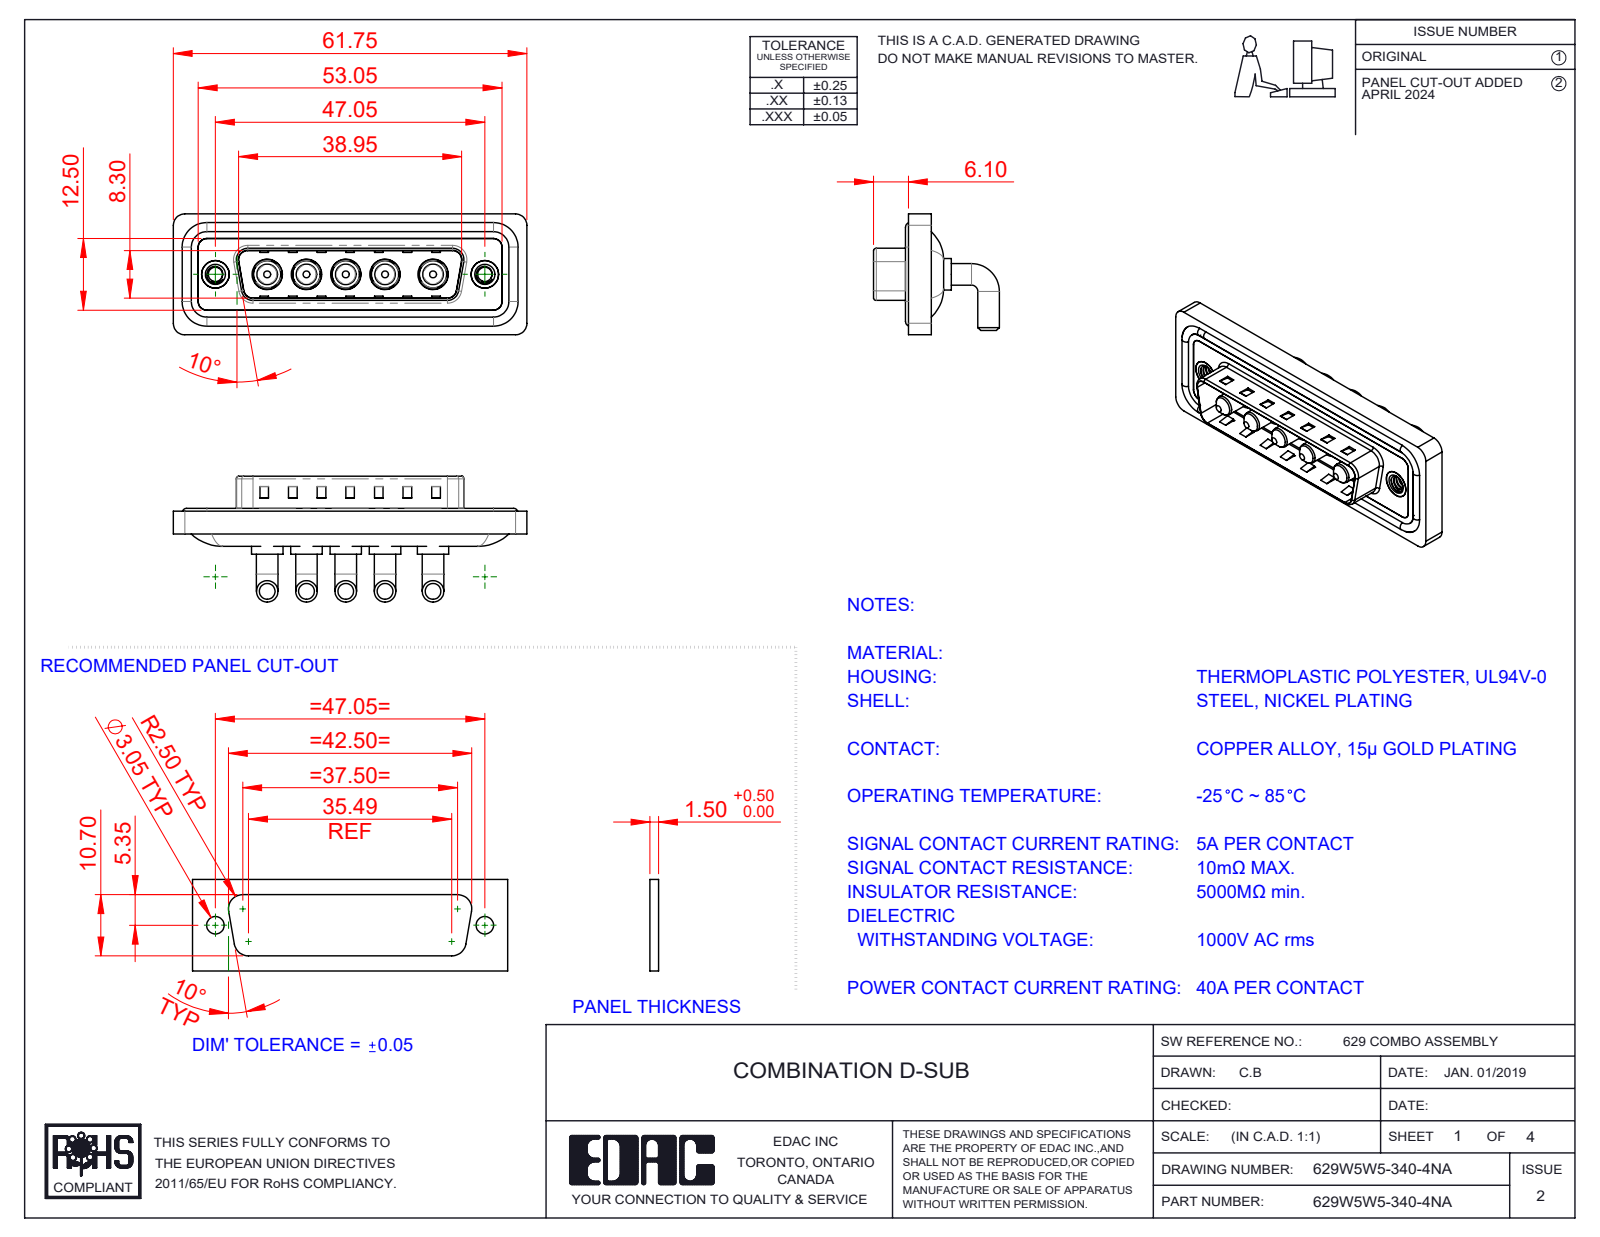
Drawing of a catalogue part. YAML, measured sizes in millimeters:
part_name: "629W5W5-340-4NA; 629Combo Waterproof Housing_25 Contacts; 629Combo Shell Rear_25 Contacts; 629Combo Threaded Rivet_A (+3 more)"
step_written_by: "SolidWorks 2023 (CONFIG_CONTROL_DESIGN)"
units: millimeters
bodies: {solids: 17, faces: 692, planar: 259, cylindrical: 291, other: 142}
overall_size: [61.75, 21.98, 21.1]
volume: 8170
surface_area: 12495
round_holes:
  - {diameter: 4.85, count: 5}
  - {diameter: 5.3, count: 5}
  - {diameter: 2.5, count: 2}
  - {diameter: 4, count: 2}
  - {diameter: 4.8, count: 2}
  - {diameter: 5, count: 2}
round_bosses_or_shafts:
  - {diameter: 3.75, count: 10}
  - {diameter: 5.5, count: 5}
  - {diameter: 5.2, count: 5}
  - {diameter: 4.75, count: 5}
  - {diameter: 3.6, count: 5}
  - {diameter: 1.6, count: 4}
  - {diameter: 4.9, count: 2}
partial_cylinders:
  - {radius: 1.5, count: 18}
  - {radius: 2, count: 18}
  - {radius: 0.5, count: 8}
  - {radius: 1.6, count: 8}
  - {radius: 2.1, count: 5}
  - {radius: 0.25, count: 4}
  - {radius: 0.6, count: 4}
  - {radius: 0.65, count: 4}
face_to_face_distances: [0.4, 2.9, 0.8, 4.5, 4.1, 1.1, 2.1, 3.1, 6, 2.5]
hole_center_spacings: [6.86, 13.73, 6.85, 6.87, 8.37, 8.38, 9.04, 9.05]
